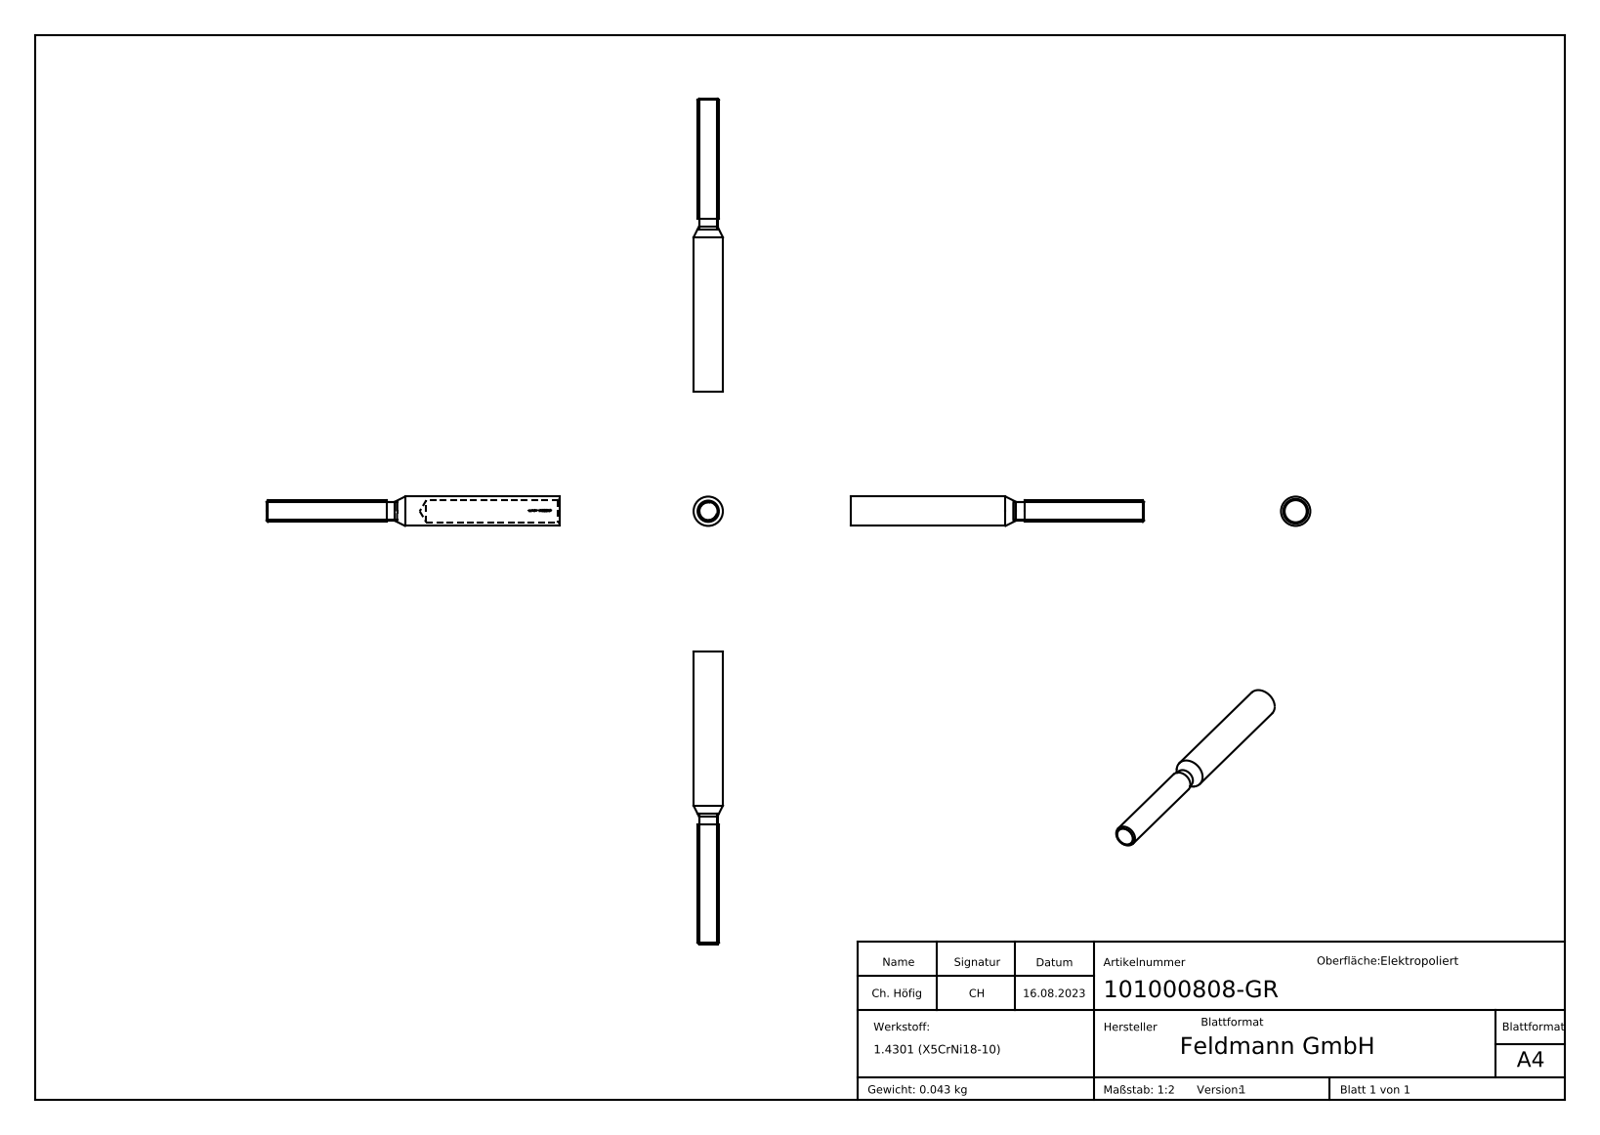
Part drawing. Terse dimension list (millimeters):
name: 101000808-GR
written by: SolidWorks 2018 (CONFIG_CONTROL_DESIGN)
unit: mm
bodies: 1 solid, 270 faces (88 planar, 37 cylindrical, 145 other)
size: 110 × 11 × 11
volume: 5 391 mm³; area: 4 787 mm²
holes: 1× ⌀8.3
bosses: 1× ⌀11, 1× ⌀8, 1× ⌀7
rounds: 1× R4.25
face distances: 110, 65, 45, 0.81, 3.88, 3.93, 8.31, 4.43, 3.62, 4.69
